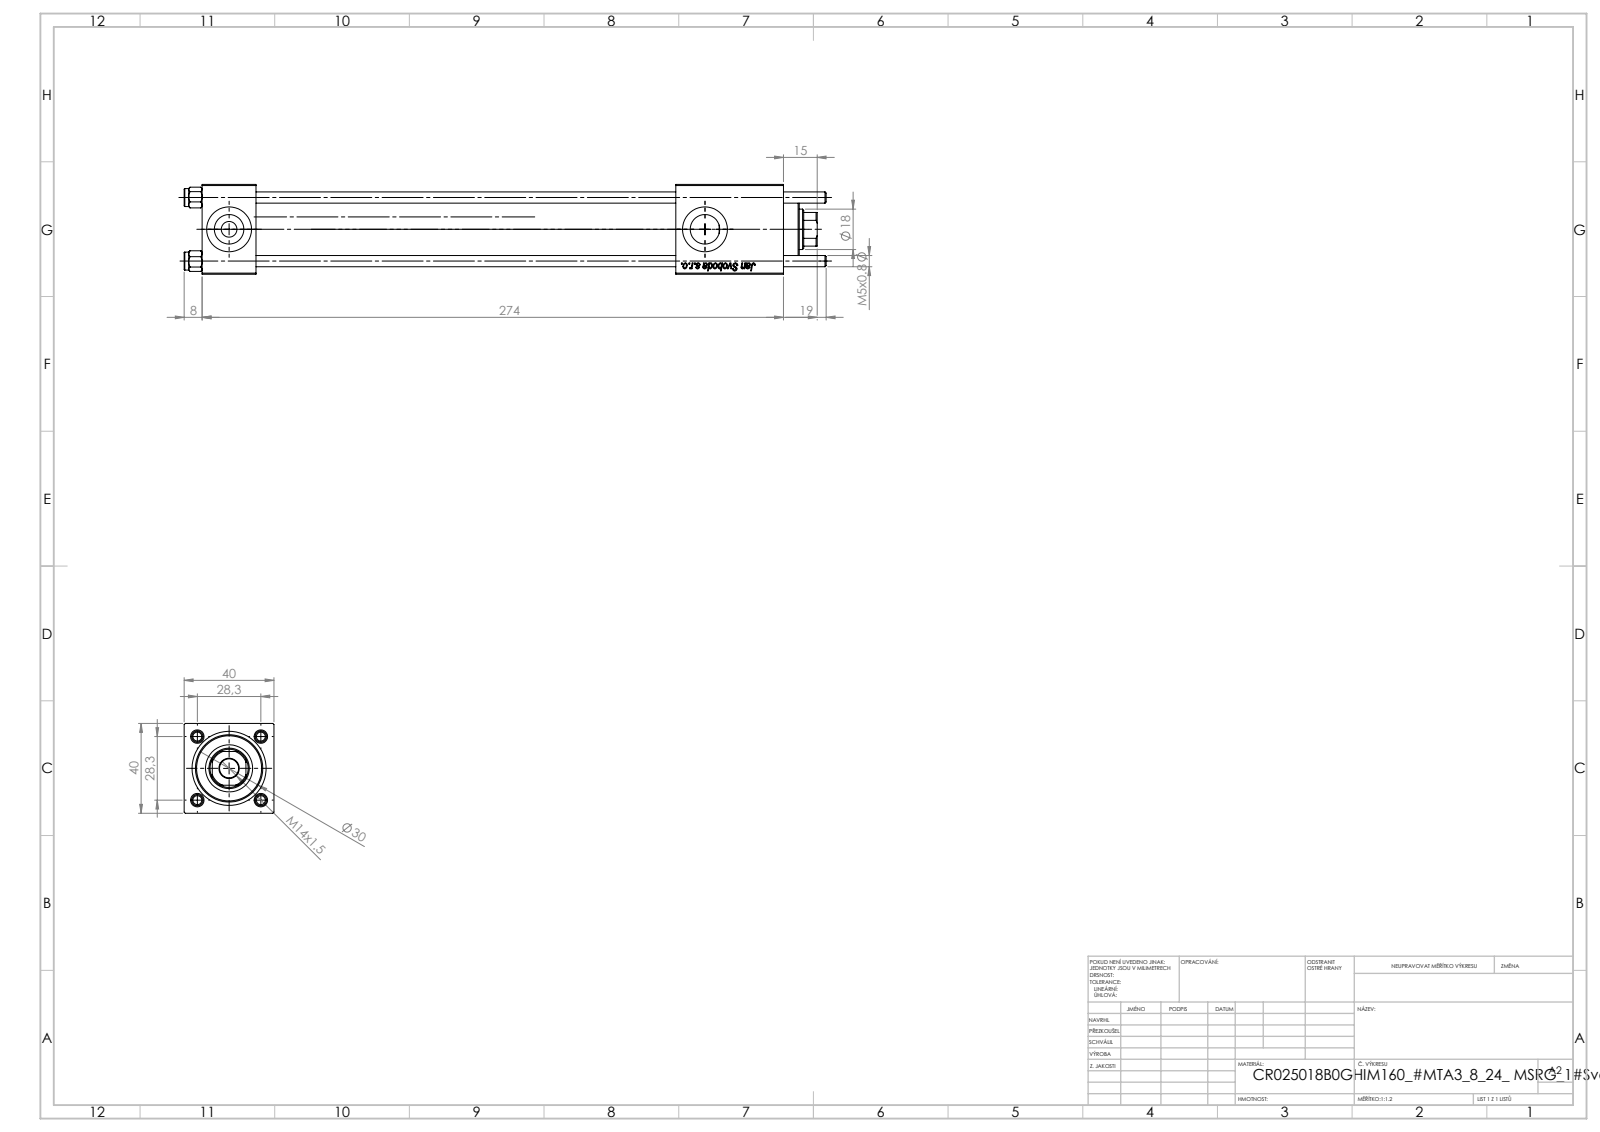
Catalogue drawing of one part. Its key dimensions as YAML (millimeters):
part_name: "V215CR_VCP_B; V215_VC_A; V215CR_B-1; NUT_M5_B (+1 more)"
step_written_by: "SolidWorks 2019 (CONFIG_CONTROL_DESIGN)"
units: millimeters
bodies: {solids: 11, faces: 1152, planar: 428, cylindrical: 76, other: 648}
overall_size: [286, 40, 40]
volume: 236057
surface_area: 102238
round_holes:
  - {diameter: 5, count: 4}
  - {diameter: 20, count: 3}
  - {diameter: 7, count: 2}
  - {diameter: 13.16, count: 2}
  - {diameter: 8.5, count: 1}
  - {diameter: 18, count: 1}
  - {diameter: 21, count: 1}
  - {diameter: 25, count: 1}
  - {diameter: 30, count: 1}
round_bosses_or_shafts:
  - {diameter: 8, count: 4}
  - {diameter: 31, count: 1}
partial_cylinders:
  - {radius: 8.5, count: 1}
face_to_face_distances: [40, 24, 211, 187, 230.3, 206.3, 19.3, 259, 235, 48]
hole_center_spacings: [20.01, 28.3, 40.02, 212]
